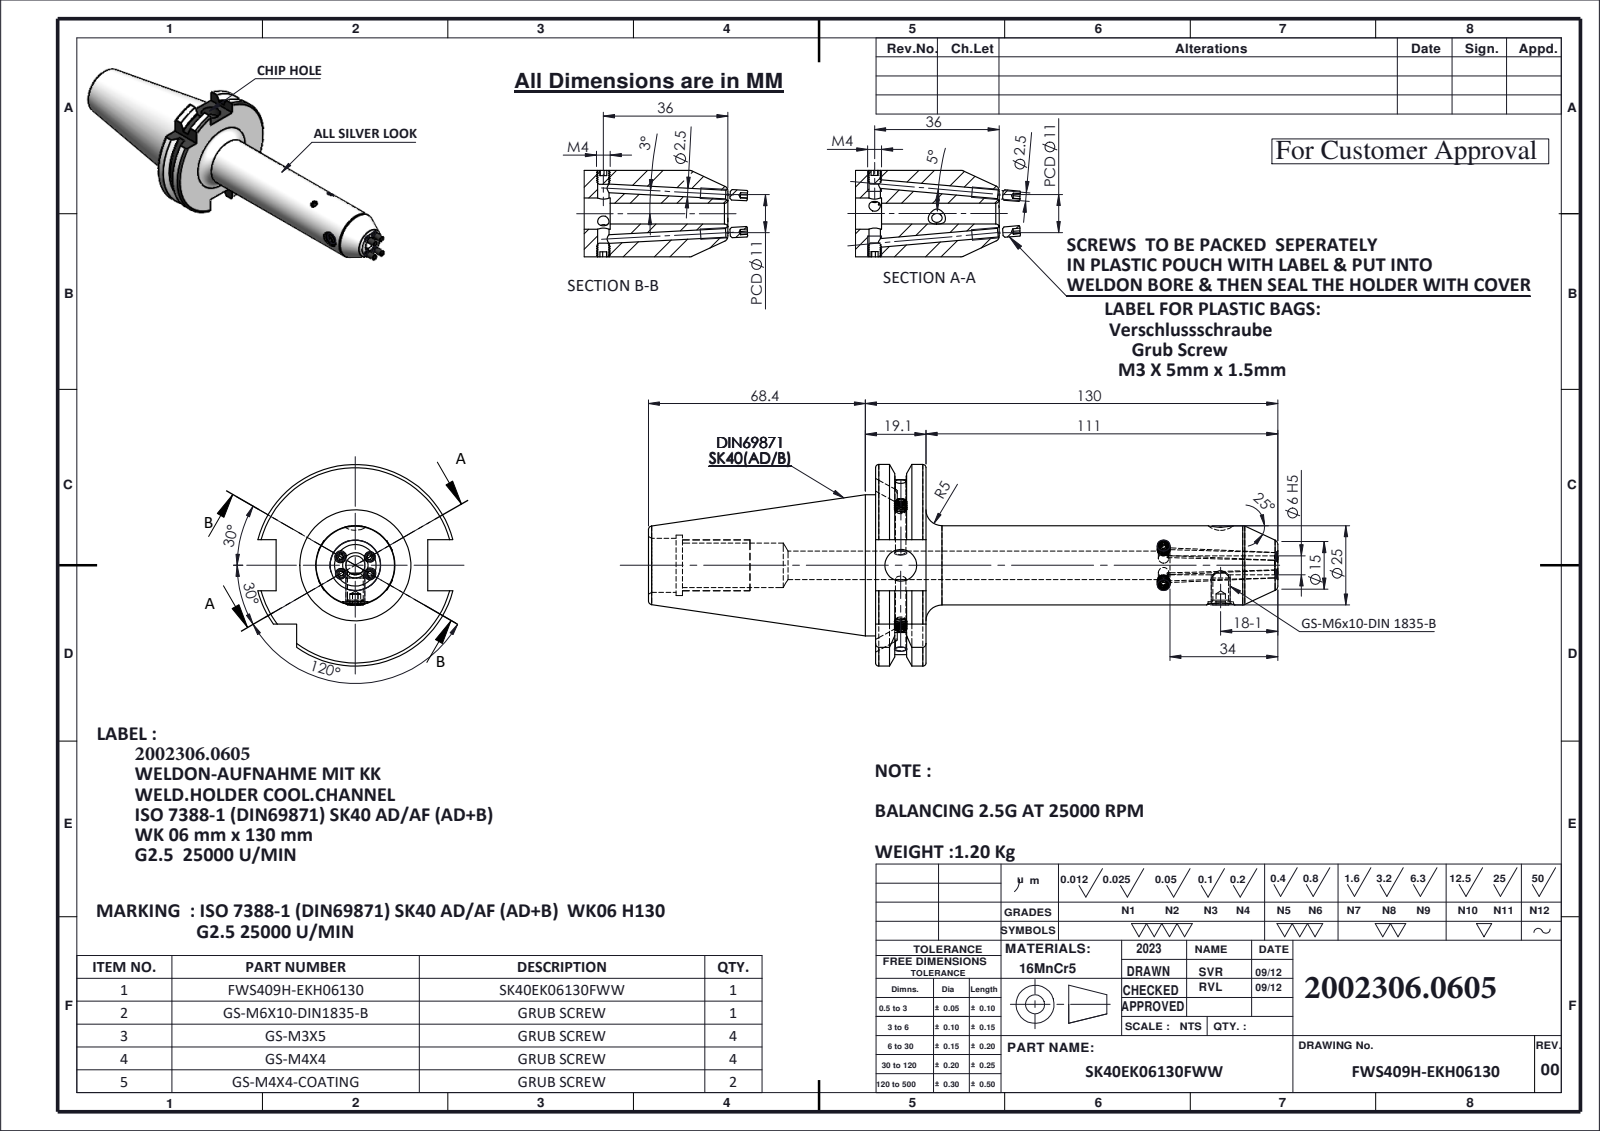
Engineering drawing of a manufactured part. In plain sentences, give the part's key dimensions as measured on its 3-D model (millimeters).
The part is named "FWS409H-EKH06130; GS-M6X10-DIN1835-B; SK40EK06130FWW; GS-M4X4_DIN 913 - M4 x 4-N (+2 more)". Its 3-D file was written by "SolidWorks 2023 (CONFIG_CONTROL_DESIGN)". It is 12 solids with 529 faces: 157 planar, 122 cylindrical and 250 other. Overall it measures 204.53 by 63.55 by 61.48 millimeters. Its volume is 148 818 cubic millimeters and its surface area 34 300 square millimeters. Round holes: 4 of diameter 2.5, 4 of diameter 3.3, 1 of diameter 5, 1 of diameter 6, 1 of diameter 8, 1 of diameter 9, 1 of diameter 10, 1 of diameter 14, 1 of diameter 17, 1 of diameter 19. Round bosses or shafts: 5 of diameter 4, 4 of diameter 3, 1 of diameter 44.45, 1 of diameter 25, 1 of diameter 6. Partial cylindrical surfaces (rounded edges, fillets, slot ends): 1 of radius 28.12, 1 of radius 31.77. The main face-to-face distances are 15.9, 16.1, 47.8, 71.6, 87.5, 10.7, 60.9, 76.8, 77.62, 66.92.
